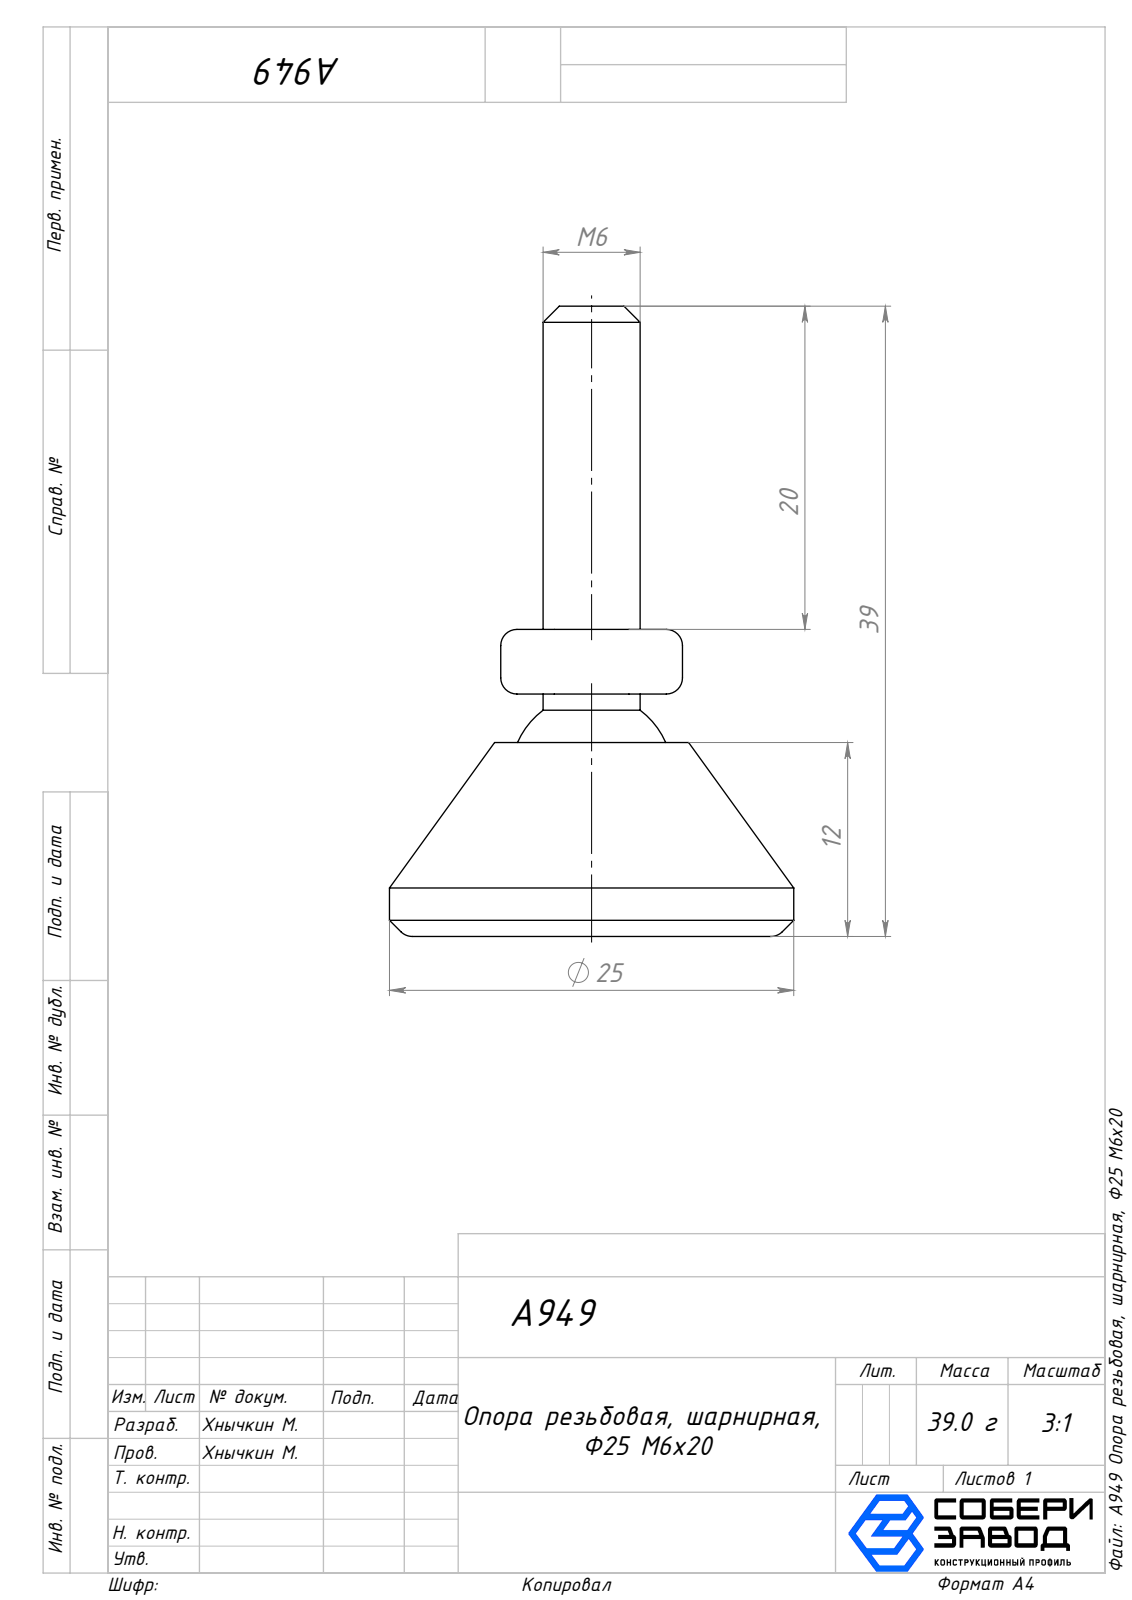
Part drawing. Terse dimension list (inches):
name: A949 Резьба_00; A949 Опора_00; A949 Опора резьбовая, шарнирная, Ф25 М6х20
written by: SolidWorks 2025 (AUTOMOTIVE_DESIGN)
unit: in
bodies: 2 solids, 59 faces (11 planar, 24 cylindrical, 24 other)
size: 1.535 × 0.984 × 0.984
volume: 0.303 in³; area: 3.883 in²
bosses: 1× ⌀0.984, 1× ⌀0.236
rounds: 18× R0.039
face distances: 0.472, 0.394, 0.591, 0.118, 0.748, 0.276, 0.157, 1.535, 1.063, 0.945
